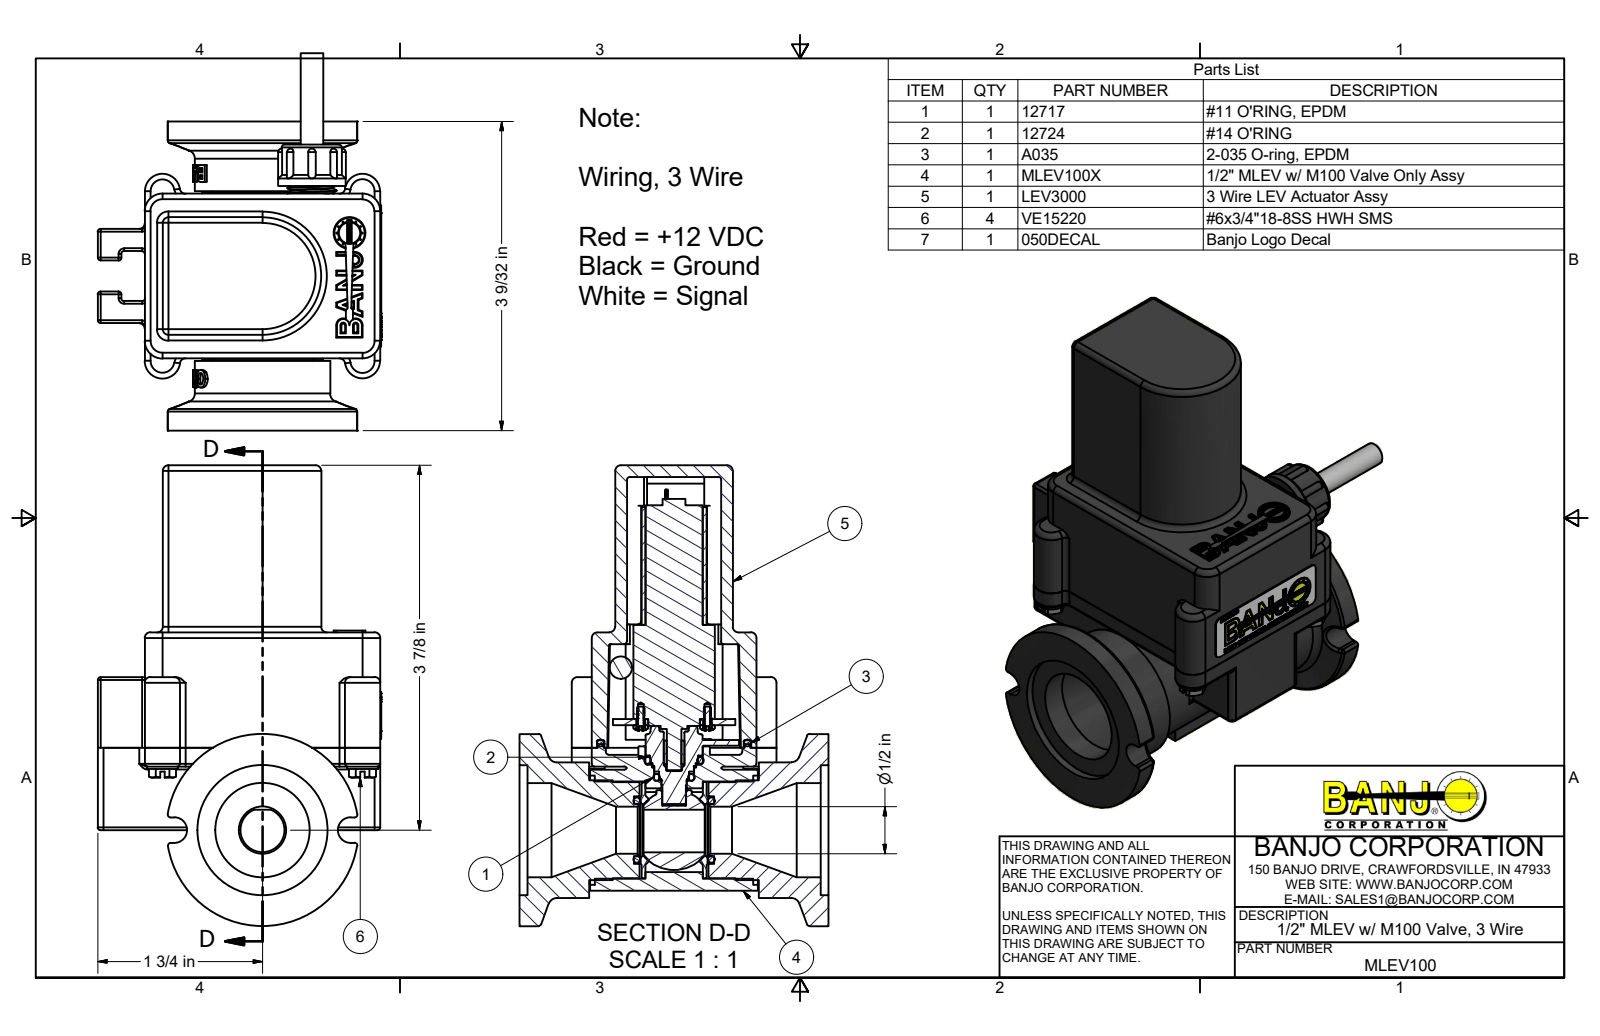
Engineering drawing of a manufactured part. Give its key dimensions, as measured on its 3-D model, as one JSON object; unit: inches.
{"part_name": "MLEV050100; VE15220; AS586A010; AS586A013 (+8 more)", "step_written_by": "Autodesk Inventor 2012 (AUTOMOTIVE_DESIGN)", "units": "inches", "bodies": {"solids": 29, "faces": 1847, "planar": 732, "cylindrical": 549, "other": 566}, "overall_size": [4.895, 3.981, 3], "volume_in3": 10.86, "surface_area_in2": 159.7, "round_holes": [[0.062, 4], [0.11, 4], [0.16, 4], [0.2, 4], [0.04, 3], [0.046, 2], [0.09, 1], [0.126, 1], [0.17, 1], [0.227, 1], [0.25, 1], [0.255, 1]], "round_bosses_or_shafts": [[0.328, 4], [0.138, 4], [0.07, 4], [0.24, 2], [2.04, 1], [1.44, 1], [1.285, 1], [1.06, 1]], "partial_cylinders_radius": [[0.03, 118], [0.015, 63], [0.06, 26], [0.01, 20], [0.125, 9], [0.04, 8], [0.188, 8], [0.25, 8]], "face_to_face_distances": [0.125, 0.22, 0.125, 0.35, 0.13, 1.35, 1.57, 1.22, 0.345, 1], "hole_center_spacings": [0.354, 0.5, 1.146, 1.195, 1.393, 1.644, 1.678, 0.15]}
